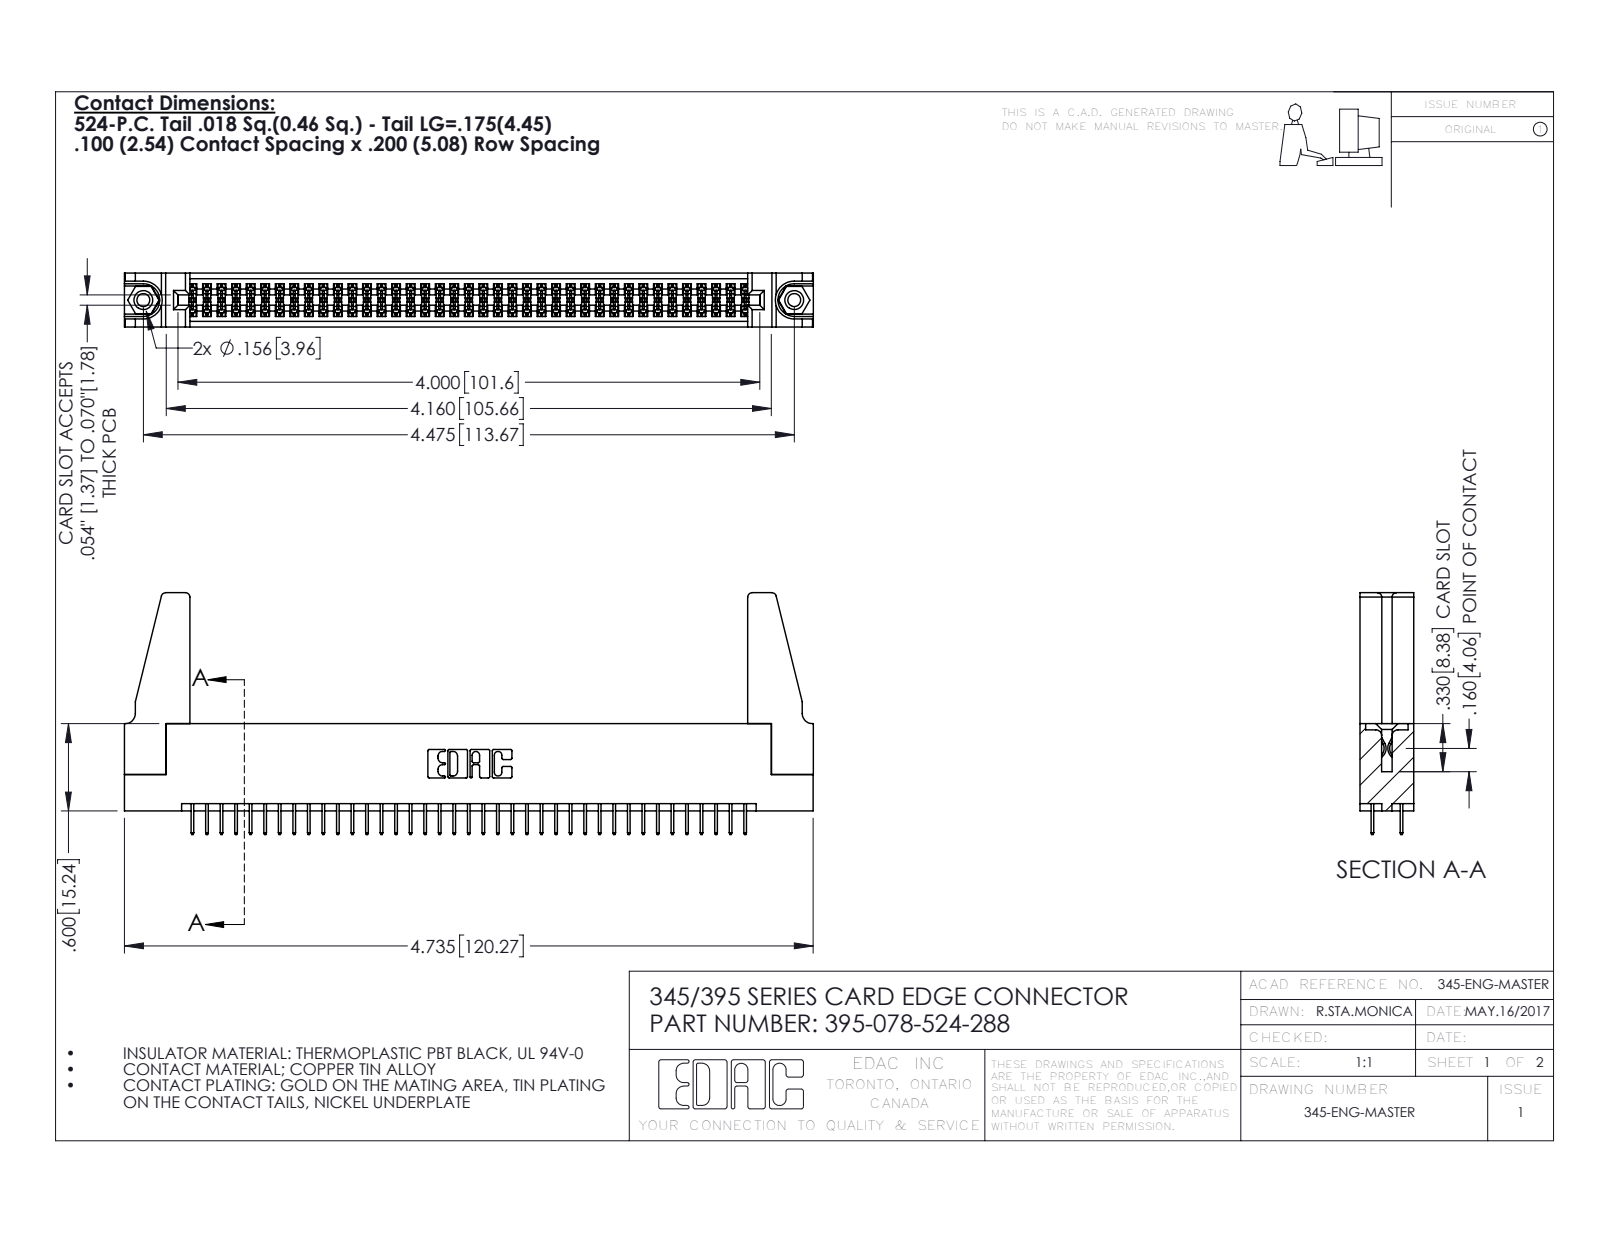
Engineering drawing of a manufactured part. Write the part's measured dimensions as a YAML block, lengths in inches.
part_name: "395-078-524-288; 345 Part_Flush Mounting Lugs - 0.156 Dia-TH; 345-250-001_345-250-001-102; 345-220-078_345-220-088 (+1 more)"
step_written_by: "SolidWorks 2016 (CONFIG_CONTROL_DESIGN)"
units: inches
bodies: {solids: 83, faces: 4462, planar: 3194, cylindrical: 1252, other: 16}
overall_size: [4.736, 1.662, 0.37]
volume: 0.903
surface_area: 30.71
round_holes:
  - {diameter: 0.089, count: 2}
  - {diameter: 0.125, count: 2}
  - {diameter: 0.156, count: 2}
  - {diameter: 0.064, count: 1}
round_bosses_or_shafts:
  - {diameter: 0.155, count: 2}
partial_cylinders:
  - {radius: 0.006, count: 117}
  - {radius: 0.01, count: 22}
  - {radius: 0.03, count: 8}
  - {radius: 0.007, count: 6}
  - {radius: 0.031, count: 6}
  - {radius: 0.026, count: 3}
  - {radius: 0.014, count: 2}
  - {radius: 0.019, count: 2}
face_to_face_distances: [0.072, 0.298, 0.37, 0.2, 0.098, 0.272, 0.025, 0.225, 0.072, 0.175]
hole_center_spacings: [0.27, 4.239, 4.475]
